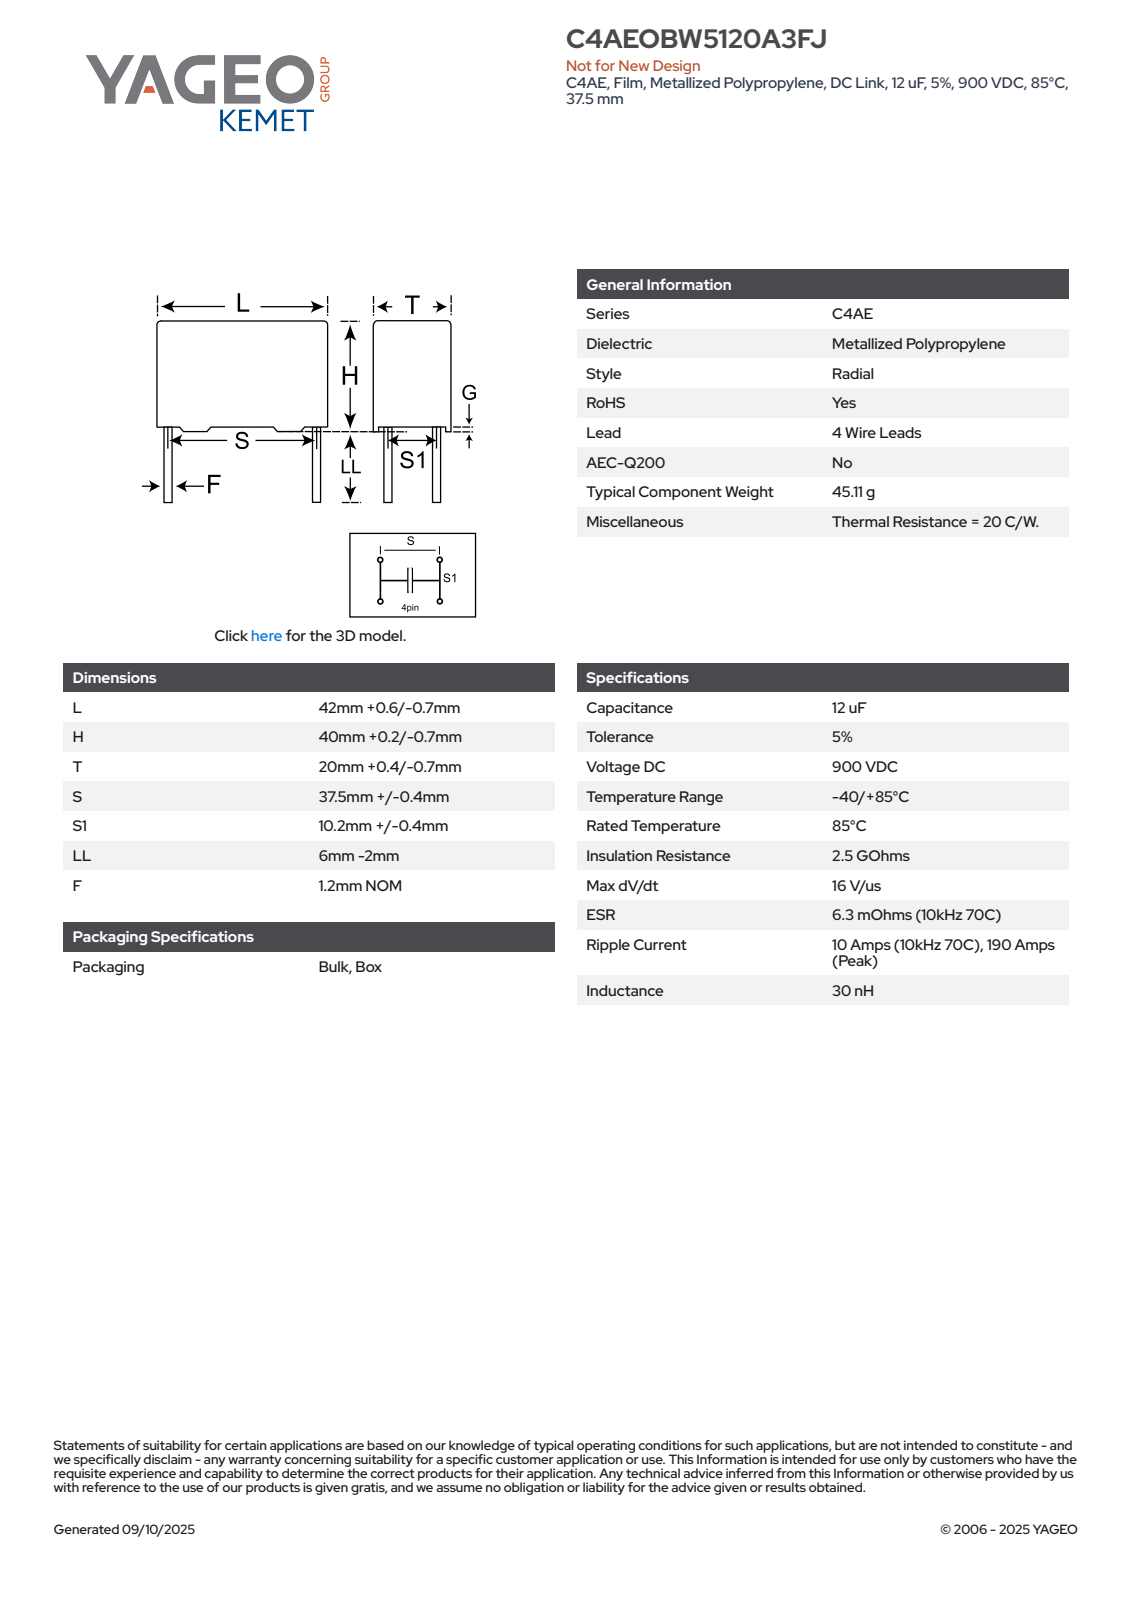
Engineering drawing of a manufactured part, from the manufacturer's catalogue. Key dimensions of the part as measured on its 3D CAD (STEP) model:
Part name (STEP PRODUCT): CFP_RB4G_42X40X20_L42.6H40.2T20.4S37.5S110.2LL4F1.2G0.5
STEP written by: SolidWorks 2014 (AUTOMOTIVE_DESIGN)
Units: millimetres
Bodies: 4 solids, 91 faces (83 planar, 8 cylindrical, 0 other)
Overall size (bounding box): 44.2 × 42.6 × 20.41
Volume: 34 548 mm³ · Surface area: 6 920 mm²
Round bosses / shafts (diameter × count): ⌀1.2 ×4
Main face-to-face distances: 20.4, 42.6, 39.7, 0.5, 40.2, 18.4, 2, 16.4, 16.84, 4
